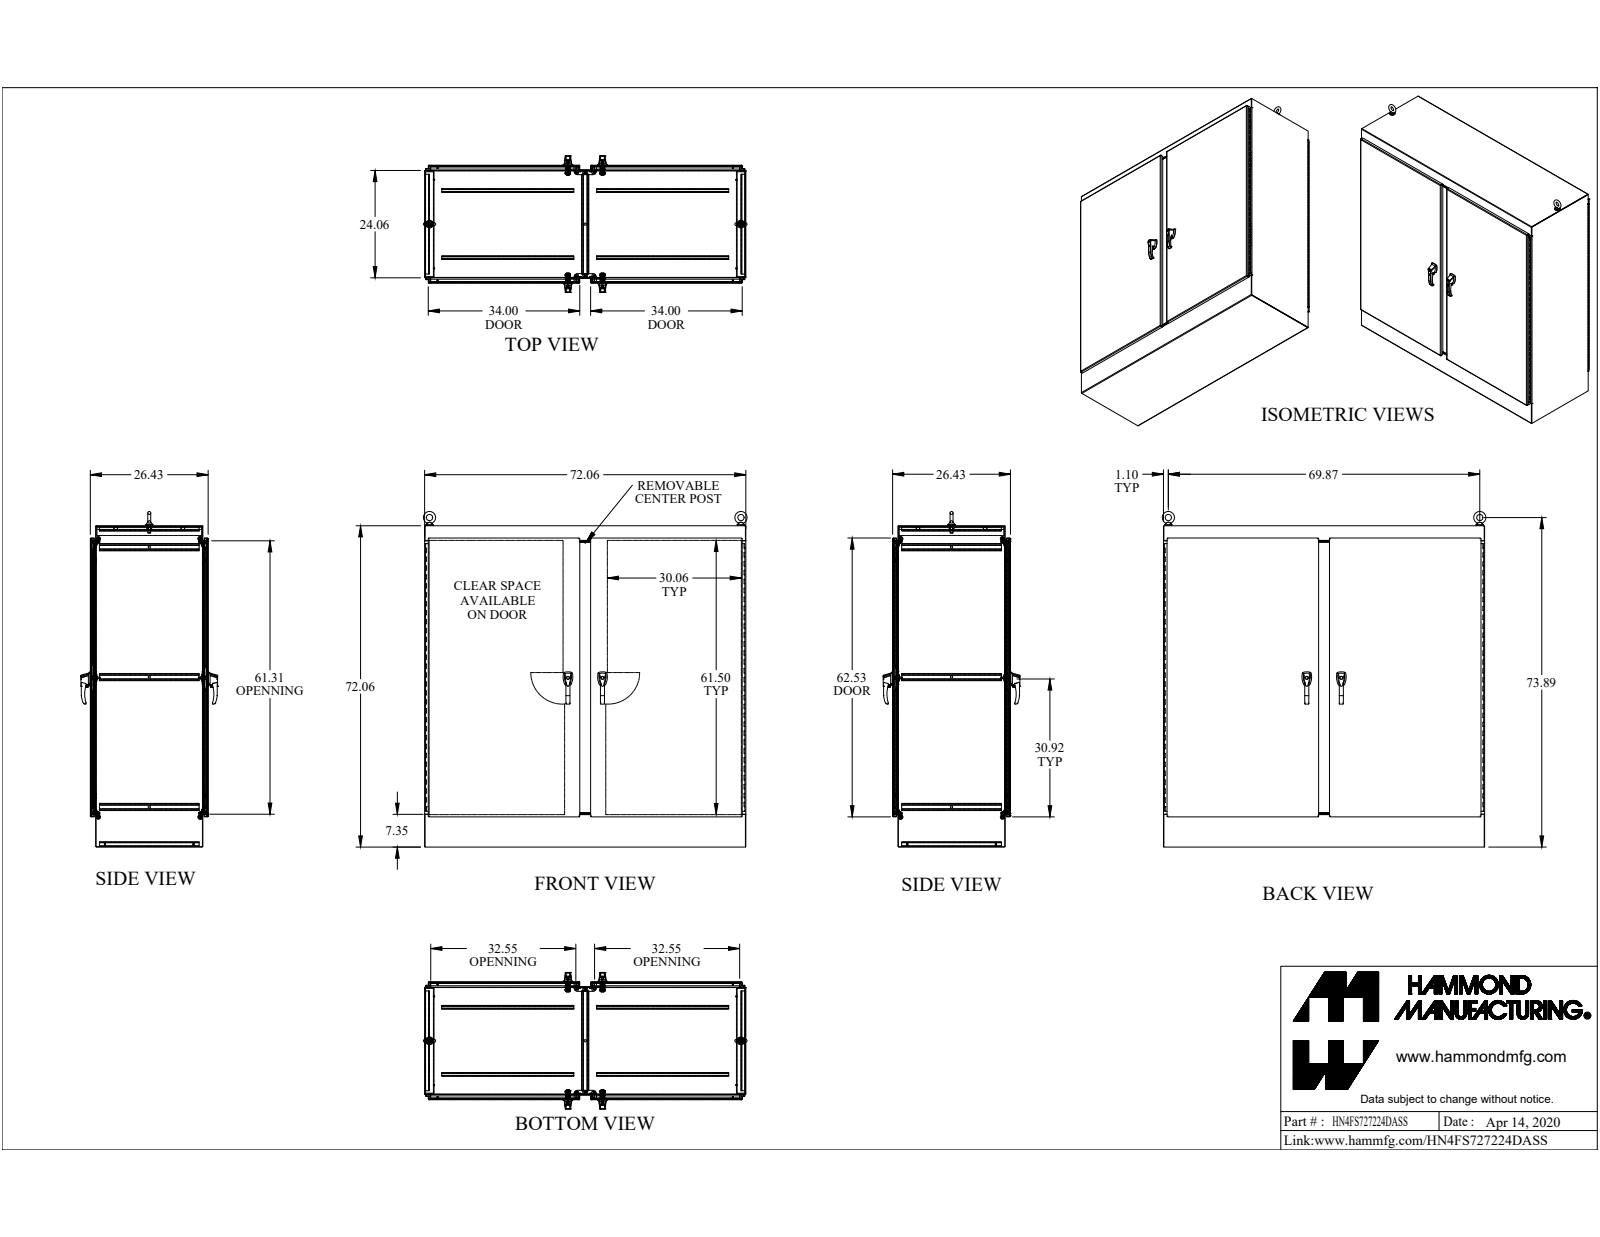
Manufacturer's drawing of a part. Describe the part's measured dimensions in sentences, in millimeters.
The part is named "HN4FS727224DASS". Its 3-D file was written by "SolidWorks 2019 (CONFIG_CONTROL_DESIGN)". It is 189 solids with 5411 faces: 2809 planar, 2126 cylindrical and 476 other. Overall it measures 1911.5 by 1844.1 by 778.9 millimeters. Its volume is 35 540 000 cubic millimeters and its surface area 29 580 000 square millimeters. Round holes: 20 of diameter 7.7, 12 of diameter 6.4, 10 of diameter 8.9, 8 of diameter 8, 6 of diameter 5.1, 6 of diameter 6.5, 6 of diameter 7.1, 6 of diameter 7.1, 6 of diameter 8, 6 of diameter 9.9, 6 of diameter 10.5, 4 of diameter 2.8. Round bosses or shafts: 8 of diameter 19.1, 8 of diameter 11.2, 6 of diameter 25.4, 6 of diameter 16, 6 of diameter 15.9, 6 of diameter 8, 6 of diameter 7.4, 6 of diameter 6.4. Partial cylindrical surfaces (rounded edges, fillets, slot ends): 60 of radius 1.1, 48 of radius 3.5, 46 of radius 2.5, 46 of radius 12.7, 42 of radius 3.2, 39 of radius 1.5, 33 of radius 8.1, 32 of radius 0.4. The main face-to-face distances are 2.4, 669, 1827.9, 666.6, 671.4, 1825.5, 30.1, 638.9, 1830.3, 32.6. The hole center spacings are 152.4, 1792.8, 304.8, 1812.2, 457.2, 1843.9, 609.6, 1887.5.
